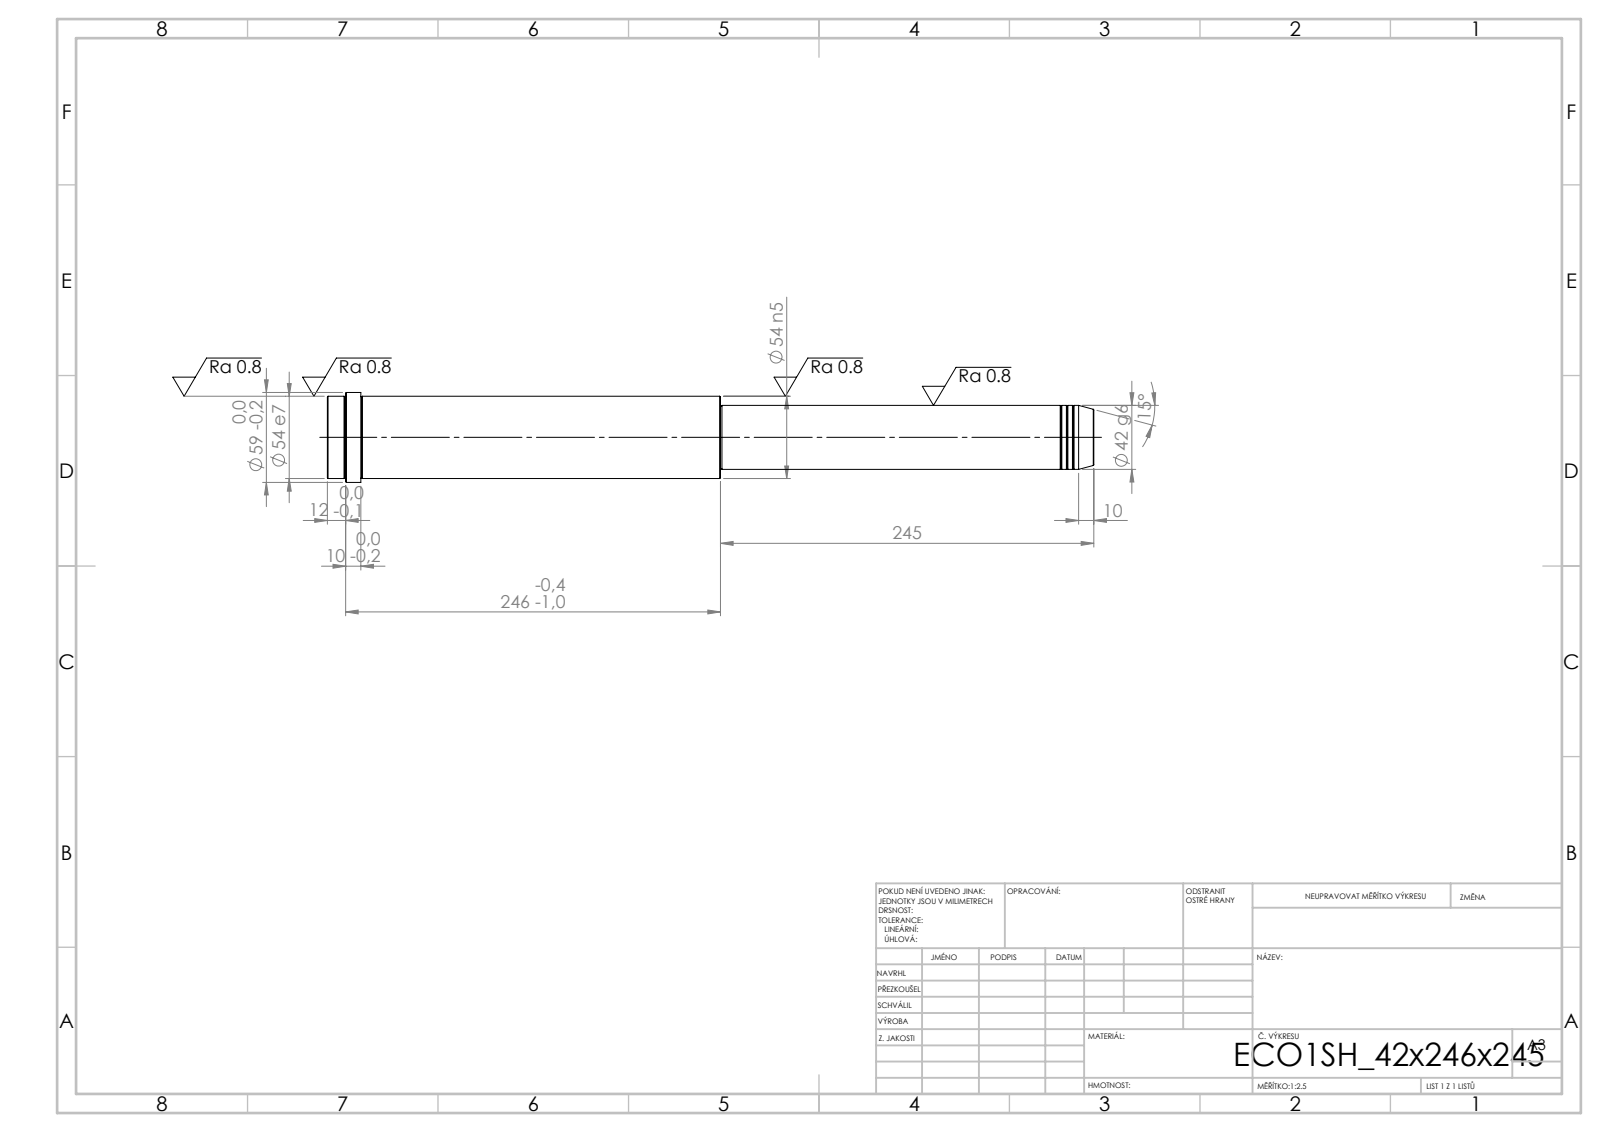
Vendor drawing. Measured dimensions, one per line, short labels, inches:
written by: SolidWorks 2019 (CONFIG_CONTROL_DESIGN)
unit: in
bodies: 1 solid, 52 faces (6 planar, 16 cylindrical, 30 other)
size: 19.803 × 2.323 × 2.323
volume: 56.91 in³; area: 126.7 in²
bosses: 1× ⌀2.323, 1× ⌀2.126, 1× ⌀1.654, 1× ⌀1.614
face distances: 19.803, 9.646, 10.157, 18.937, 9.291, 0.866, 19.331, 9.685, 0.394, 0.472
